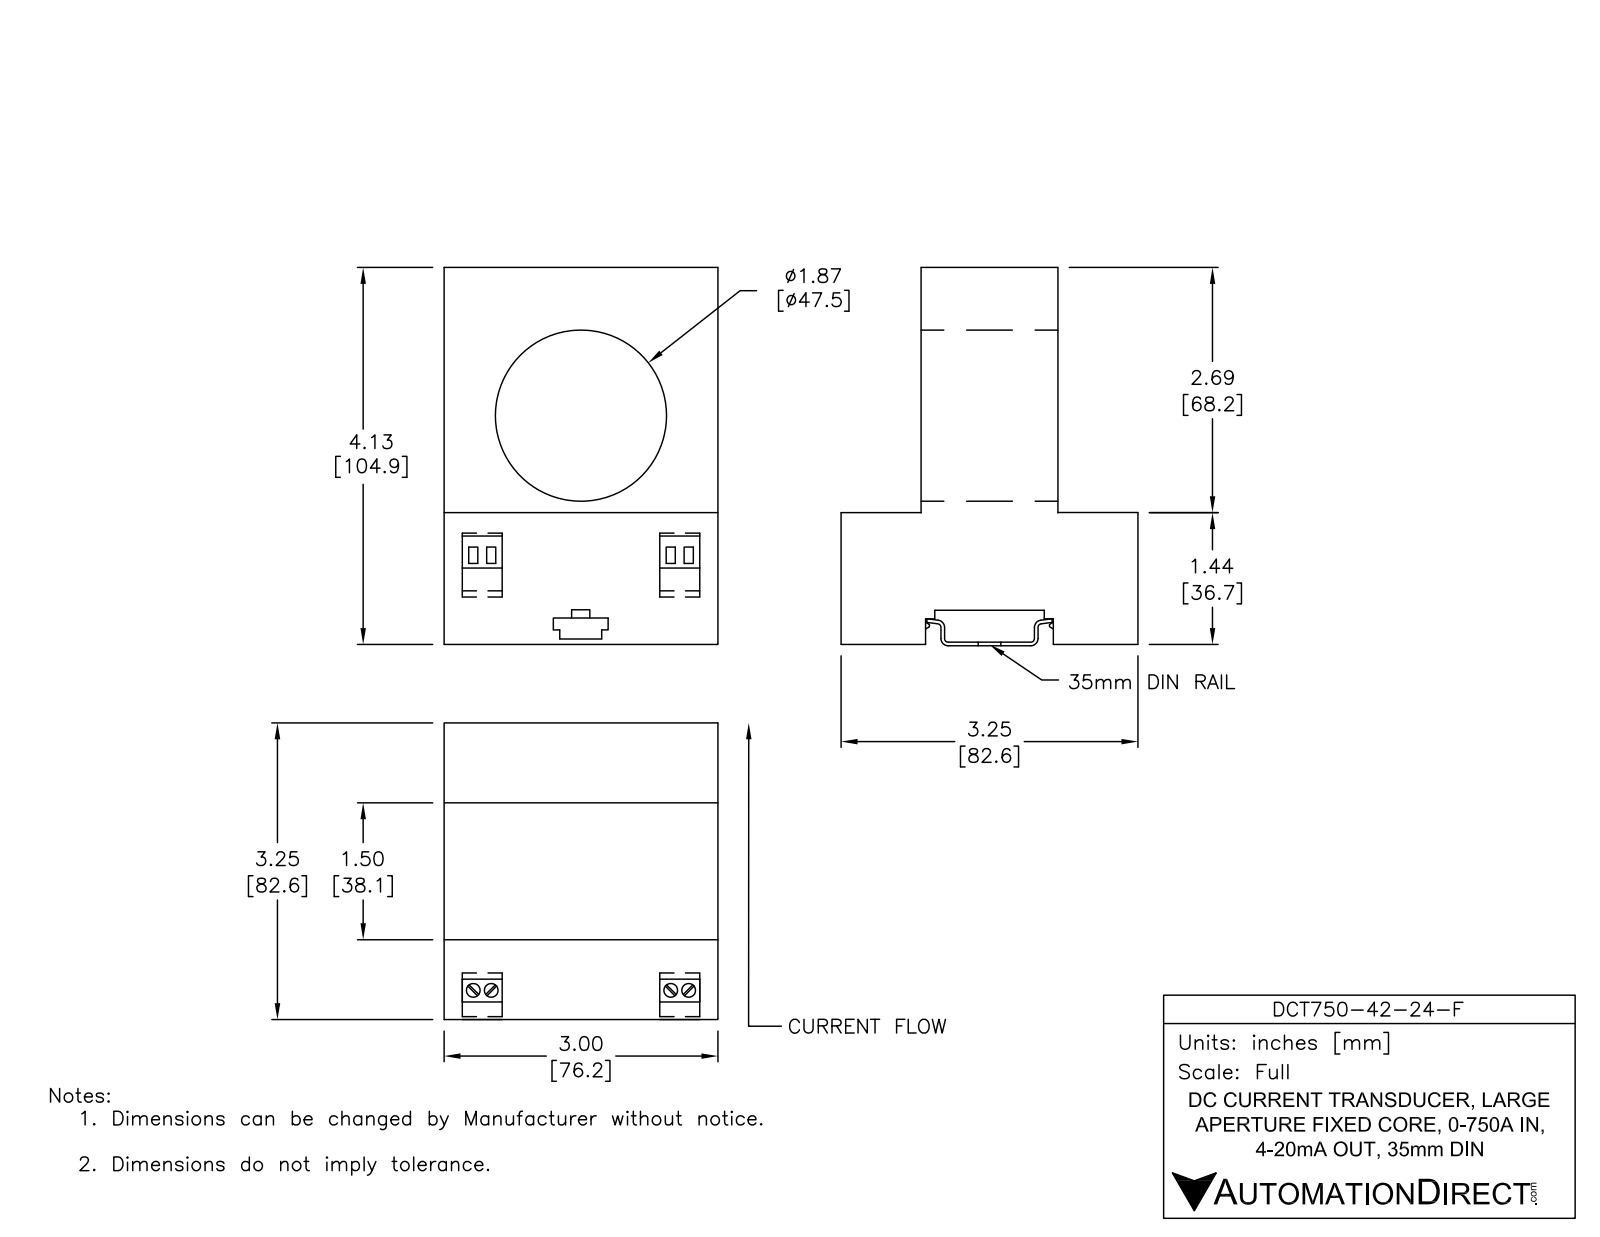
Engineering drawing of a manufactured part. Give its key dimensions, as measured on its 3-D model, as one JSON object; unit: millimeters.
{"part_name": "DCT750-42-24-F", "step_written_by": "SolidWorks 2017 (AUTOMOTIVE_DESIGN)", "units": "millimeters", "bodies": {"solids": 13, "faces": 360, "planar": 310, "cylindrical": 50, "other": 0}, "overall_size": [106.7, 89.5, 76.2], "volume_mm3": 230200, "surface_area_mm2": 71100, "round_holes": [[5.2, 4], [2.5, 2], [46.2, 1]], "round_bosses_or_shafts": [[4.7, 4]], "partial_cylinders_radius": [[2.5, 4], [3.3, 4], [4.5, 4]], "face_to_face_distances": [1.9, 1.9, 76.2, 30.6, 28.7, 38.1, 31.8, 29.8, 1.1, 60.2], "hole_center_spacings": [10, 44.1, 65.4, 68.7, 17.2, 17.2, 27.1, 27.1]}
